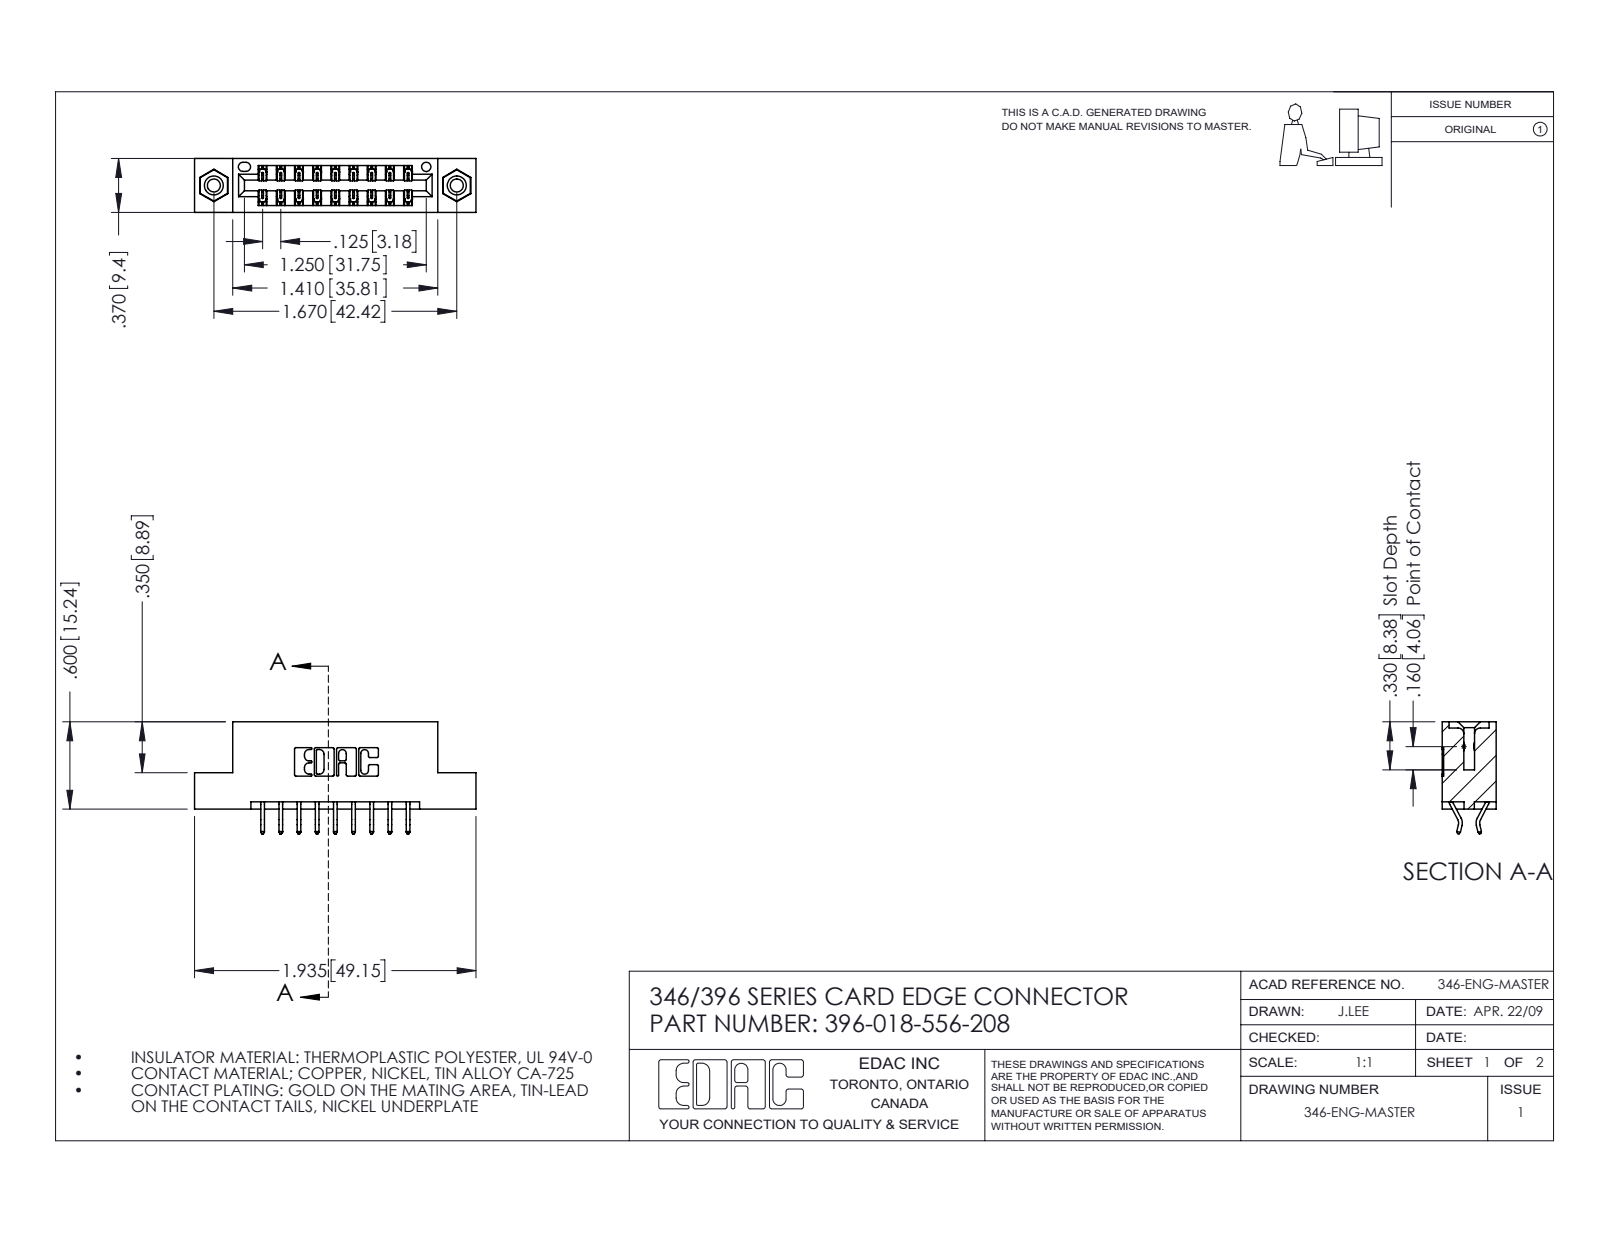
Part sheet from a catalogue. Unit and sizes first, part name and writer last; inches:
Units: inches
Overall size (bounding box): 1.935 × 0.77 × 0.37
Round holes (diameter × count): ⌀0.089 ×2, ⌀0.125 ×2, ⌀0.156 ×2, ⌀0.064 ×1
Round bosses / shafts (diameter × count): ⌀0.155 ×2
Partial cylindrical surfaces — rounded edges, fillets, slot ends (radius × count): R0.006 ×27, R0.01 ×22, R0.007 ×6, R0.031 ×6, R0.026 ×3, R0.01 ×2, R0.014 ×2, R0.022 ×2
Main face-to-face distances: 0.25, 0.048, 0.322, 0.37, 0.025, 0.148, 0.222, 0.1, 0.174, 0.072
Hole centre spacings: 0.246, 1.465, 1.67
Volume: 0.276 in³ · Surface area: 8.851 in²
Bodies: 21 solids, 1226 faces (810 planar, 400 cylindrical, 16 other)
Part name (STEP PRODUCT): 346 Part_Flush Mounting Lugs - 0.156 Dia-TI; 345-250-001_345-250-003-102; 345-292-001_556 Tail; 396-018-556-208
STEP written by: SolidWorks 2016 (CONFIG_CONTROL_DESIGN)
